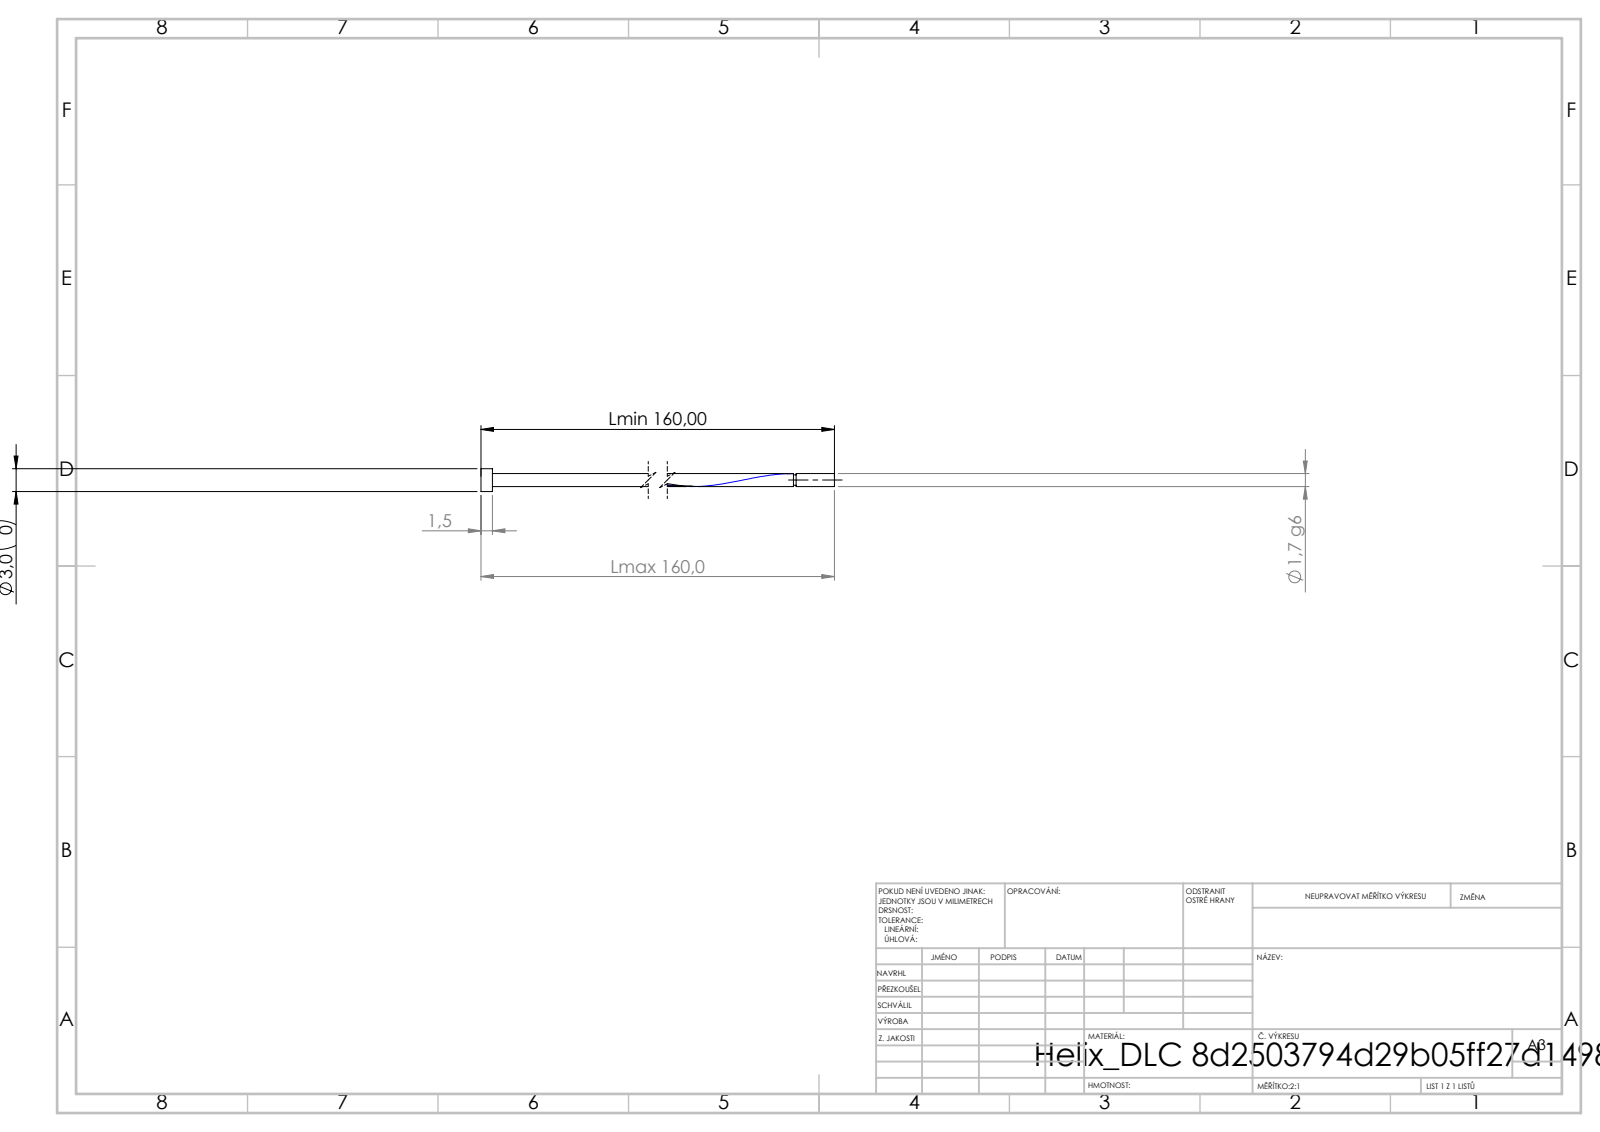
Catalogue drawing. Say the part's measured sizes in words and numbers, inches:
Its 3-D file was written by "SolidWorks 2019 (CONFIG_CONTROL_DESIGN)". It is 1 solid with 16 faces: 6 planar, 9 cylindrical and 1 other. Overall it measures 6.299 by 0.118 by 0.118 inches. Its volume is 0.027 cubic inches and its surface area 1.82 square inches. Round bosses or shafts: 1 of diameter 0.118, 1 of diameter 0.067, 1 of diameter 0.054. The main face-to-face distances are 0.059, 6.299, 6.24, 6.101, 6.042, 0.198, 6.088, 6.029, 0.013, 0.211.
